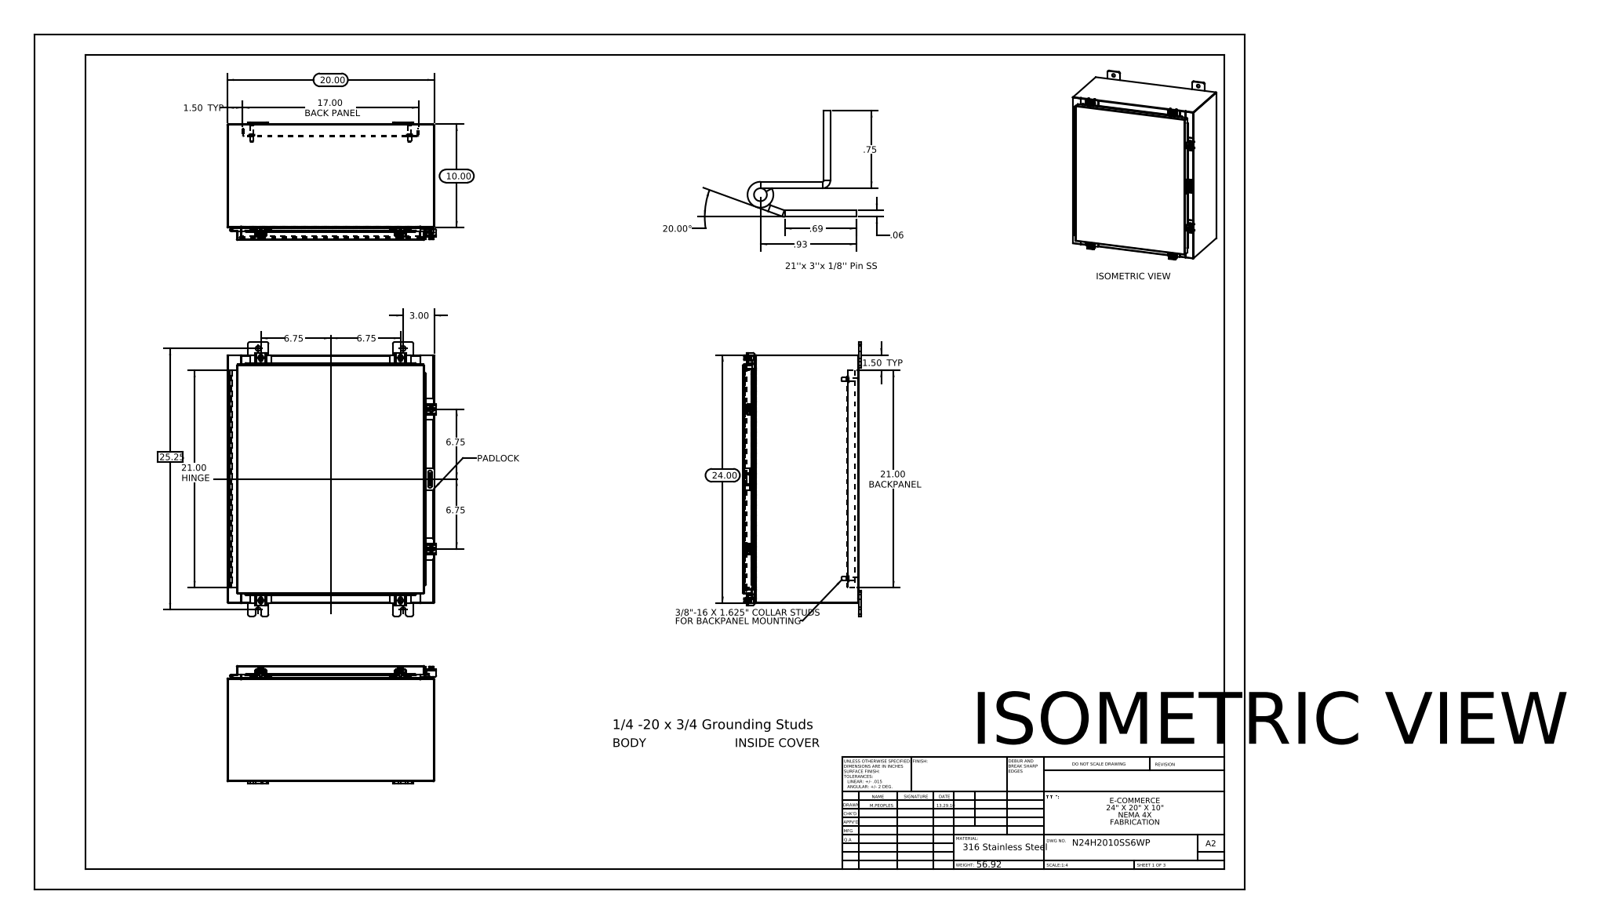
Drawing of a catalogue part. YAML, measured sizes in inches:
part_name: "N24H2010SS6WP Clamp Top; N24H2010SS6WP Hinge Cover Side; N24H2010SS6WP Clamp Assembly; N24H2010SS6WP Hinge Enclosure Side2 (+8 more)"
step_written_by: "SolidWorks 2013 (CONFIG_CONTROL_DESIGN)"
units: inches
bodies: {solids: 47, faces: 1709, planar: 908, cylindrical: 705, other: 96}
overall_size: [26.5, 20.211, 11.389]
volume: 200
surface_area: 5063
round_holes:
  - {diameter: 0.5, count: 8}
  - {diameter: 0.213, count: 6}
  - {diameter: 0.26, count: 6}
  - {diameter: 0.125, count: 2}
  - {diameter: 0.125, count: 1}
round_bosses_or_shafts:
  - {diameter: 0.25, count: 7}
  - {diameter: 0.5, count: 6}
  - {diameter: 0.399, count: 6}
  - {diameter: 0.625, count: 4}
  - {diameter: 0.375, count: 4}
  - {diameter: 0.33, count: 4}
partial_cylinders:
  - {radius: 0.06, count: 30}
  - {radius: 0.013, count: 25}
  - {radius: 0.19, count: 24}
  - {radius: 0.088, count: 21}
  - {radius: 0.12, count: 12}
  - {radius: 0.141, count: 12}
  - {radius: 0.125, count: 10}
  - {radius: 0.05, count: 9}
face_to_face_distances: [0.075, 11.126, 19.925, 11.201, 11.051, 23.925, 0.104, 1, 1.075, 10.051]
hole_center_spacings: [21.369, 25.739, 13.5, 0.431, 0.934, 1.858, 2.275, 2.276]
